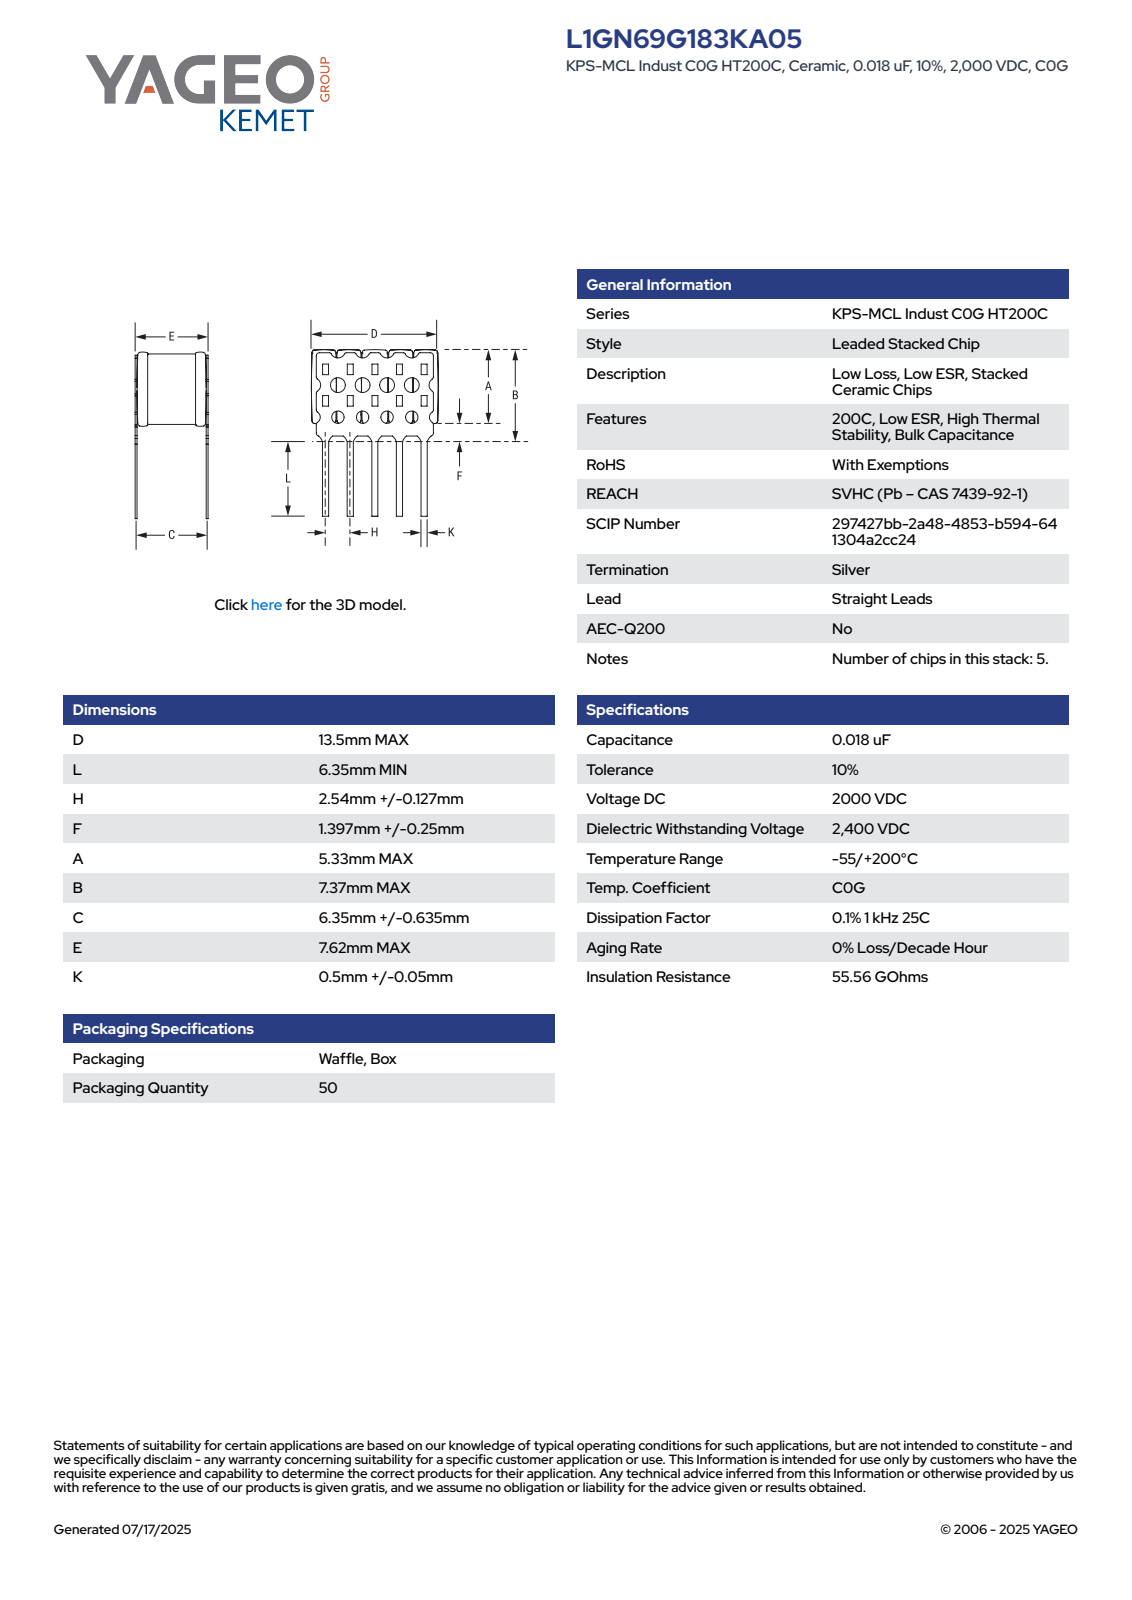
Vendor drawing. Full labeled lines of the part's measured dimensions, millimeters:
Part name (STEP PRODUCT): CCSS_KLSS5_D13.5L6.35H2.667F1.647A5.33B7.37C6.985E7.62K0.55
STEP written by: SolidWorks 2014 (AUTOMOTIVE_DESIGN)
Units: millimetres
Bodies: 7 solids, 238 faces (238 planar, 0 cylindrical, 0 other)
Overall size (bounding box): 14.22 × 9.74 × 7.37
Volume: 532 mm³ · Surface area: 706 mm²
Main face-to-face distances: 5.69, 2.85, 2.84, 5.49, 6.99, 2.64, 5.62, 5.52, 5.89, 2.65
